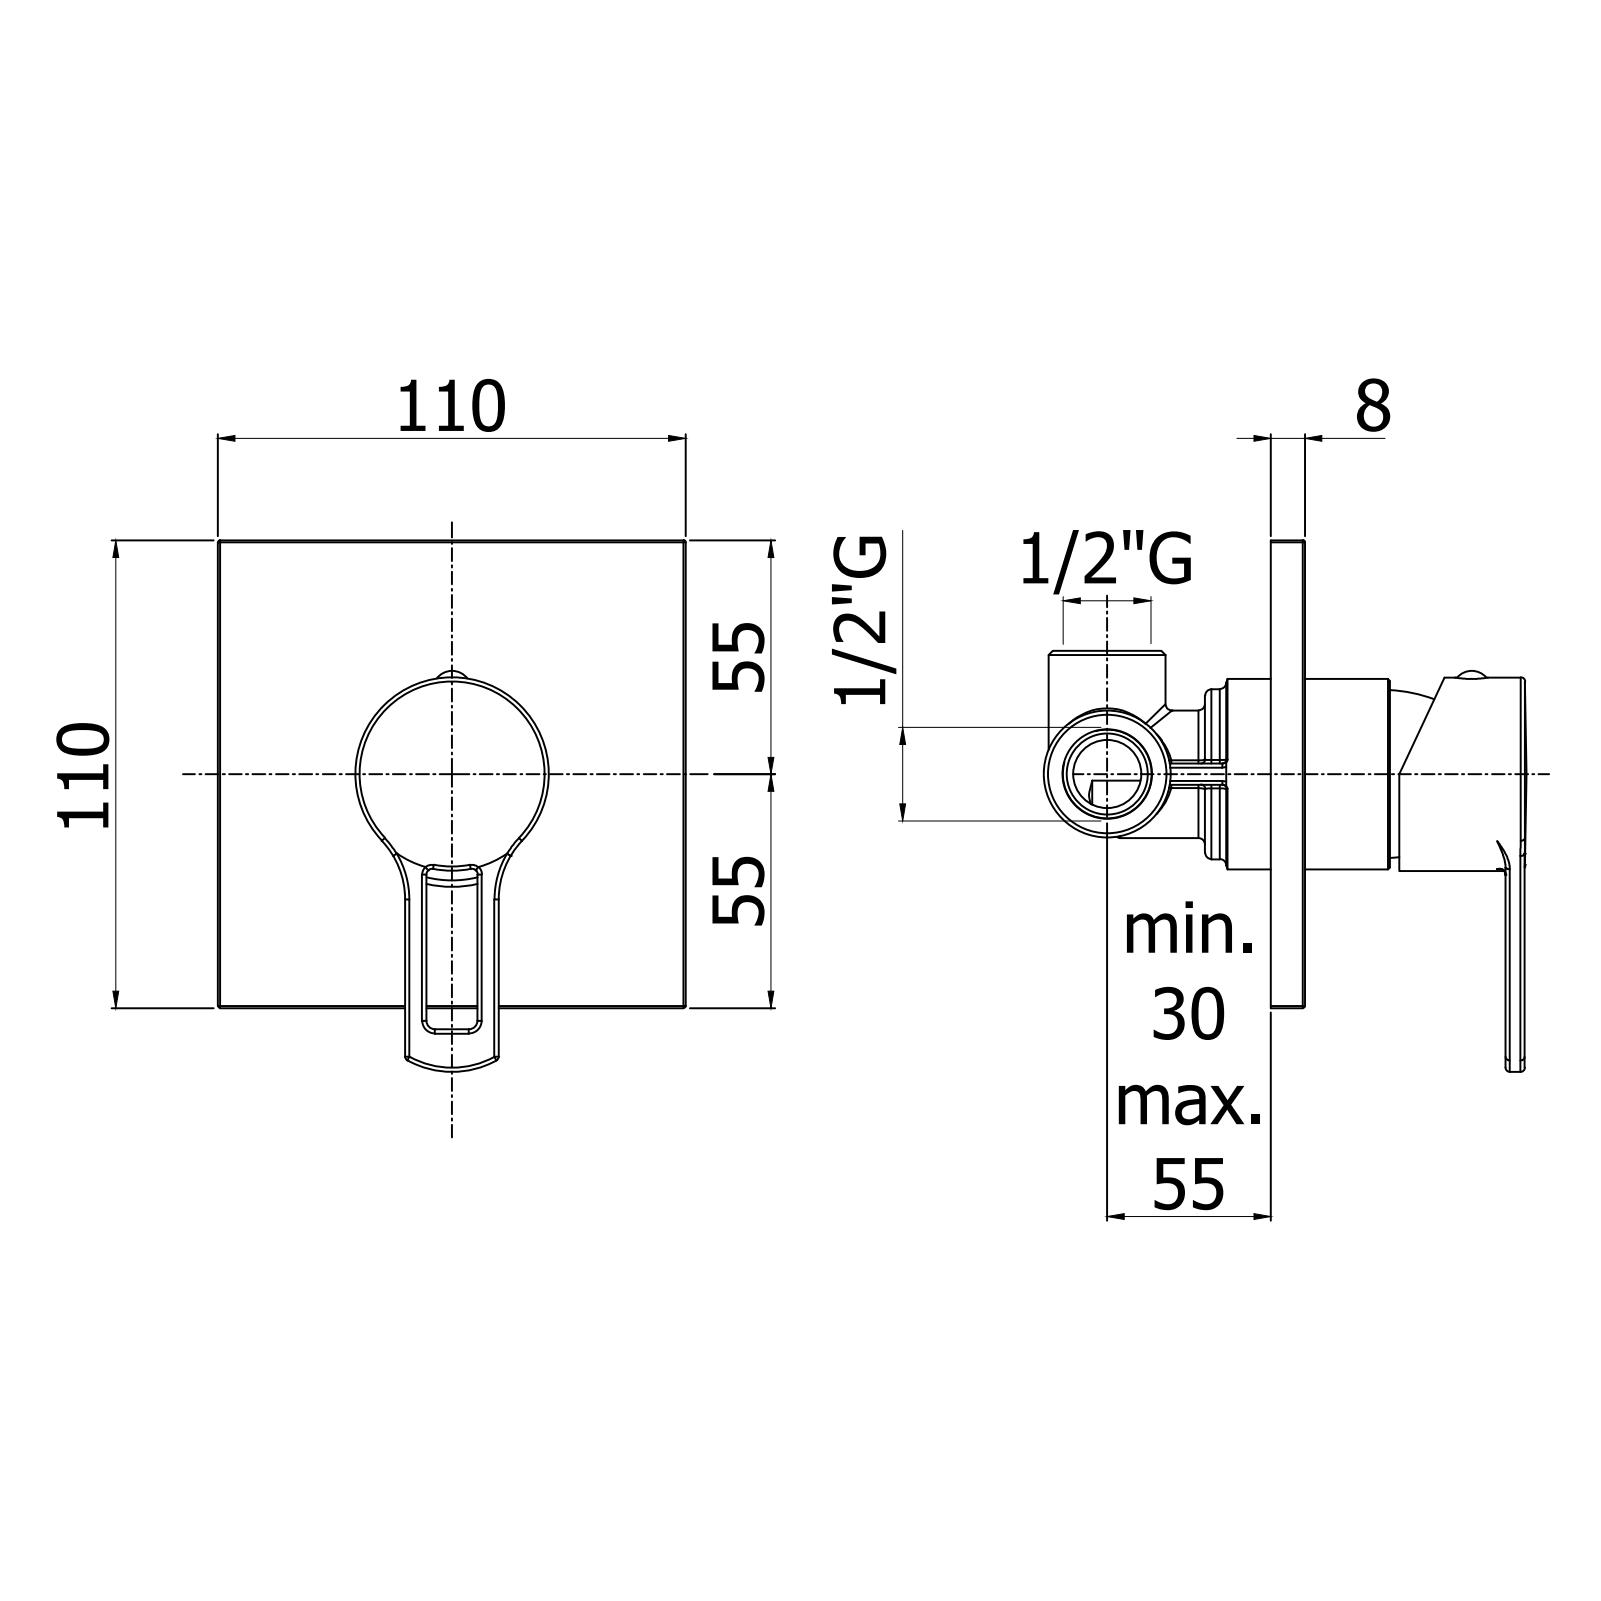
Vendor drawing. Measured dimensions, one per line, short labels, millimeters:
name: RIN010CR
written by: CREO PARAMETRIC BY PTC INC, 2020044 (CONFIG_CONTROL_DESIGN)
unit: mm
bodies: 2 solids, 1084 faces (604 planar, 262 cylindrical, 218 other)
size: 144.95 × 110 × 59.6
volume: 110 143 mm³; area: 70 183 mm²
holes: 2× ⌀4, 1× ⌀3, 1× ⌀3.3, 1× ⌀5, 1× ⌀7.8, 1× ⌀19.5, 1× ⌀19.9, 1× ⌀26.8, 1× ⌀29, 1× ⌀31, 1× ⌀32.4, 1× ⌀36
bosses: 2× ⌀44.8, 1× ⌀51, 1× ⌀49, 1× ⌀35, 1× ⌀32.2, 1× ⌀23.5, 1× ⌀23.4, 1× ⌀21.8
rounds: 50× R0.5, 18× R1, 11× R0.15, 8× R2, 4× R0.3, 2× R20, 1× R7, 1× R9.3
face distances: 7, 2, 1, 6, 0.5, 5, 53.6, 8, 22, 108
hole spacings: 11
